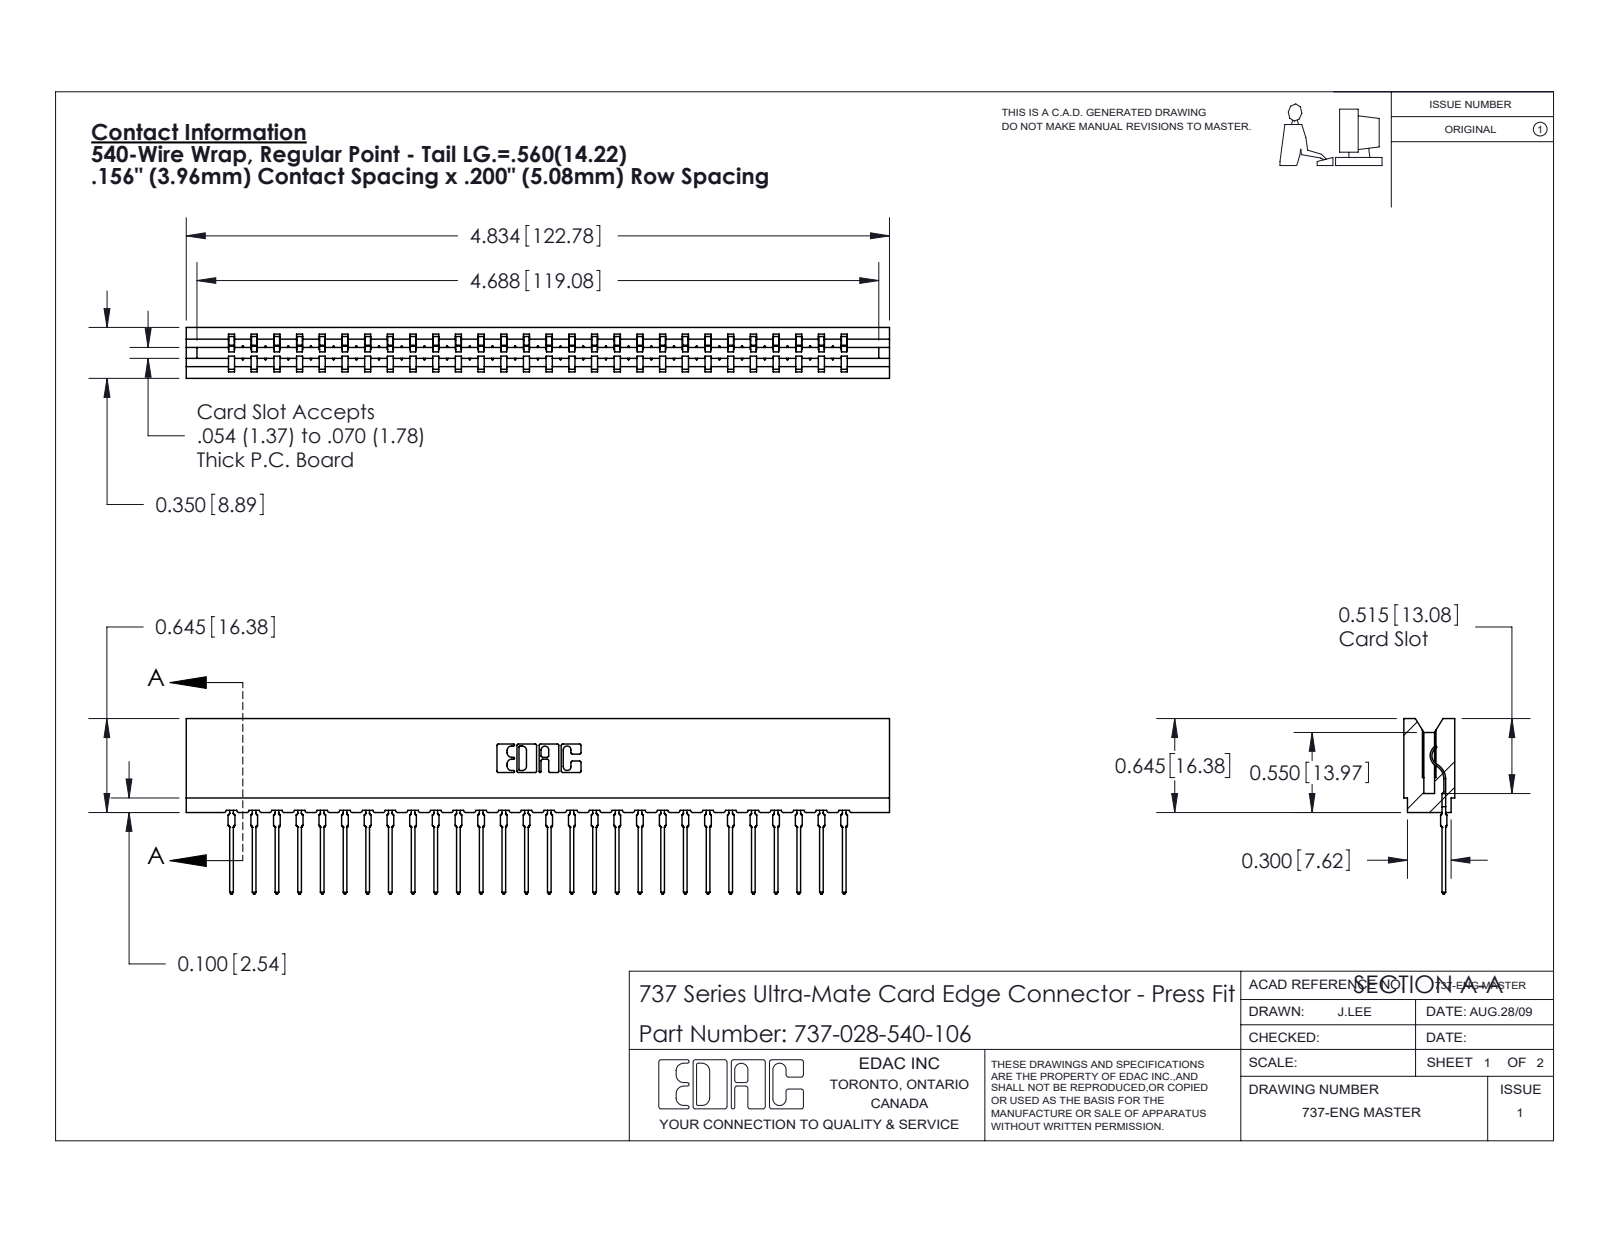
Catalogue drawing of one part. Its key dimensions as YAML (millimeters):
part_name: "745-292-001_540; 737-028-540-106; 737 Part_Insulator Option - 06"
step_written_by: "SolidWorks 2020 (CONFIG_CONTROL_DESIGN)"
units: millimeters
bodies: {solids: 29, faces: 3259, planar: 1959, cylindrical: 572, other: 728}
overall_size: [122.8, 30.6, 8.9]
volume: 12000
surface_area: 16230
partial_cylinders:
  - {radius: 0.4, count: 56}
  - {radius: 0.5, count: 56}
  - {radius: 0.3, count: 22}
  - {radius: 0.2, count: 6}
  - {radius: 0.8, count: 6}
  - {radius: 0.1, count: 4}
  - {radius: 0.3, count: 4}
  - {radius: 0.7, count: 3}
face_to_face_distances: [3.5, 5.4, 8.9, 1.9, 4, 1.1, 7.7, 2.4, 4.2, 15.8]
